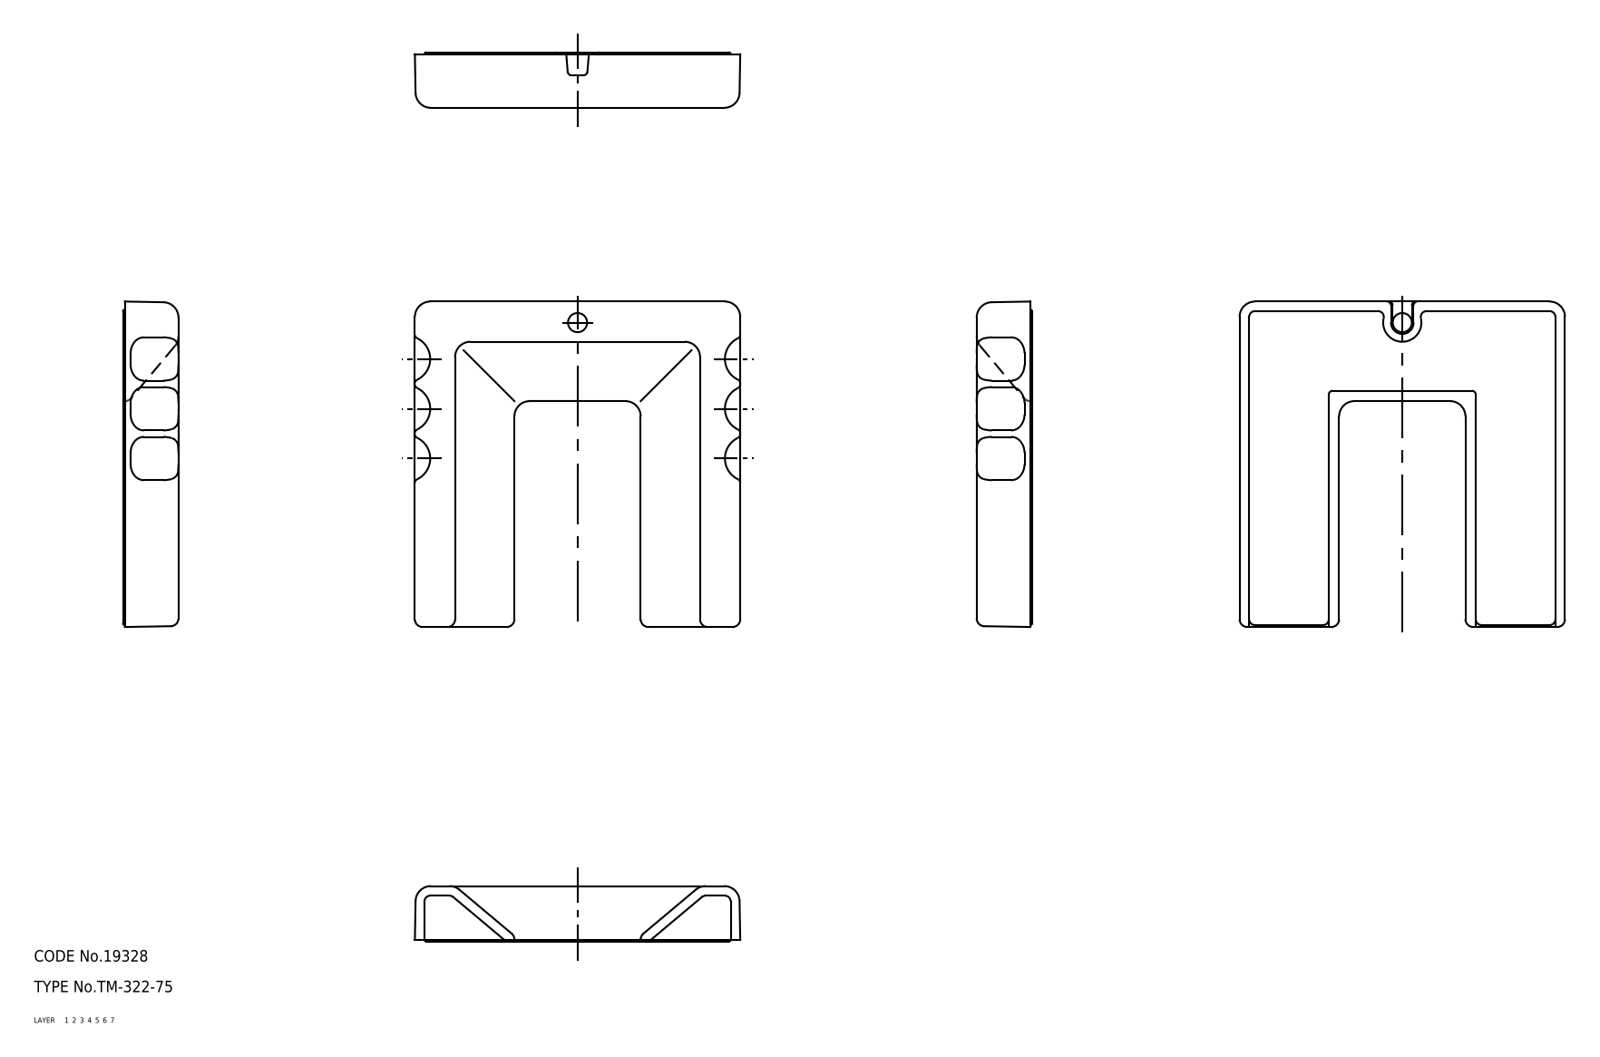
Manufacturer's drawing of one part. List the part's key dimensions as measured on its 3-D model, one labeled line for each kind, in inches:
Part name (STEP PRODUCT): 67123309; 67123322
STEP written by: CADfix (AUTOMOTIVE_DESIGN)
Units: inches
Bodies: 2 solids, 200 faces (0 planar, 0 cylindrical, 200 other)
Overall size (bounding box): 3.346 × 3.346 × 0.571
Volume: 3.342 in³ · Surface area: 38.38 in²
